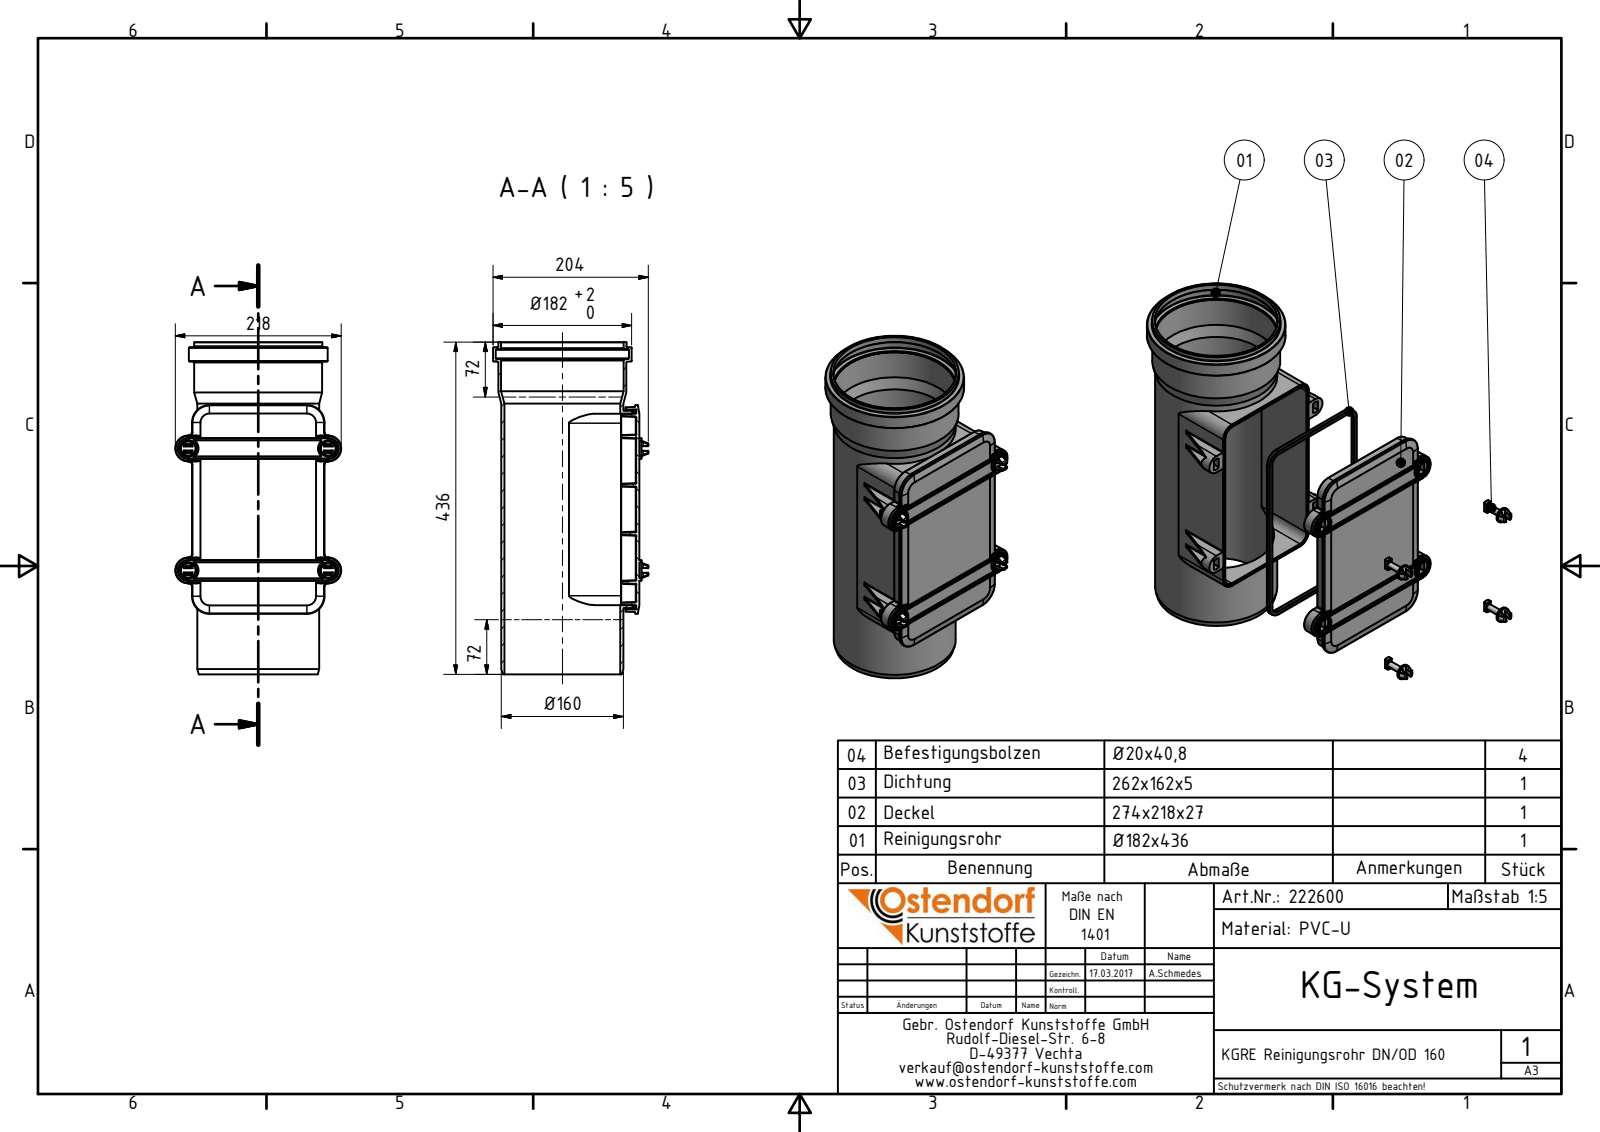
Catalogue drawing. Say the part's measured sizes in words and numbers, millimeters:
The part is named "222600 KGRE Reinigungsrohr eckig DN_OD 160; 222600 KGRE Reinigungsrohr eckig DN_OD 160 Deckel; 222600 KGRE Reinigungsrohr eckig DN_OD 160 Dichtung; 222600 KGRE Reinigungsrohr DN_OD 160 Befestigung (+1 more)". Its 3-D file was written by "Autodesk Inventor 2016 (AUTOMOTIVE_DESIGN)". It is 7 solids with 1512 faces: 358 planar, 543 cylindrical and 611 other. Overall it measures 436 by 218 by 204 millimeters. Its volume is 1 297 000 cubic millimeters and its surface area 679 430 square millimeters. Round holes: 4 of diameter 21, 1 of diameter 152, 1 of diameter 160.8, 1 of diameter 161.1, 1 of diameter 174.8. Round bosses or shafts: 4 of diameter 20, 4 of diameter 7.9, 1 of diameter 182, 1 of diameter 168.3, 1 of diameter 168, 1 of diameter 160.2. Partial cylindrical surfaces (rounded edges, fillets, slot ends): 124 of radius 0.5, 108 of radius 1, 16 of radius 4, 8 of radius 0.3, 8 of radius 2, 8 of radius 3.5, 6 of radius 13, 4 of radius 7.95. The main face-to-face distances are 4, 155, 151, 159, 63.64, 47.96, 5, 127.28, 97.9, 49.94. The hole center spacings are 160, 184, 243.84.
